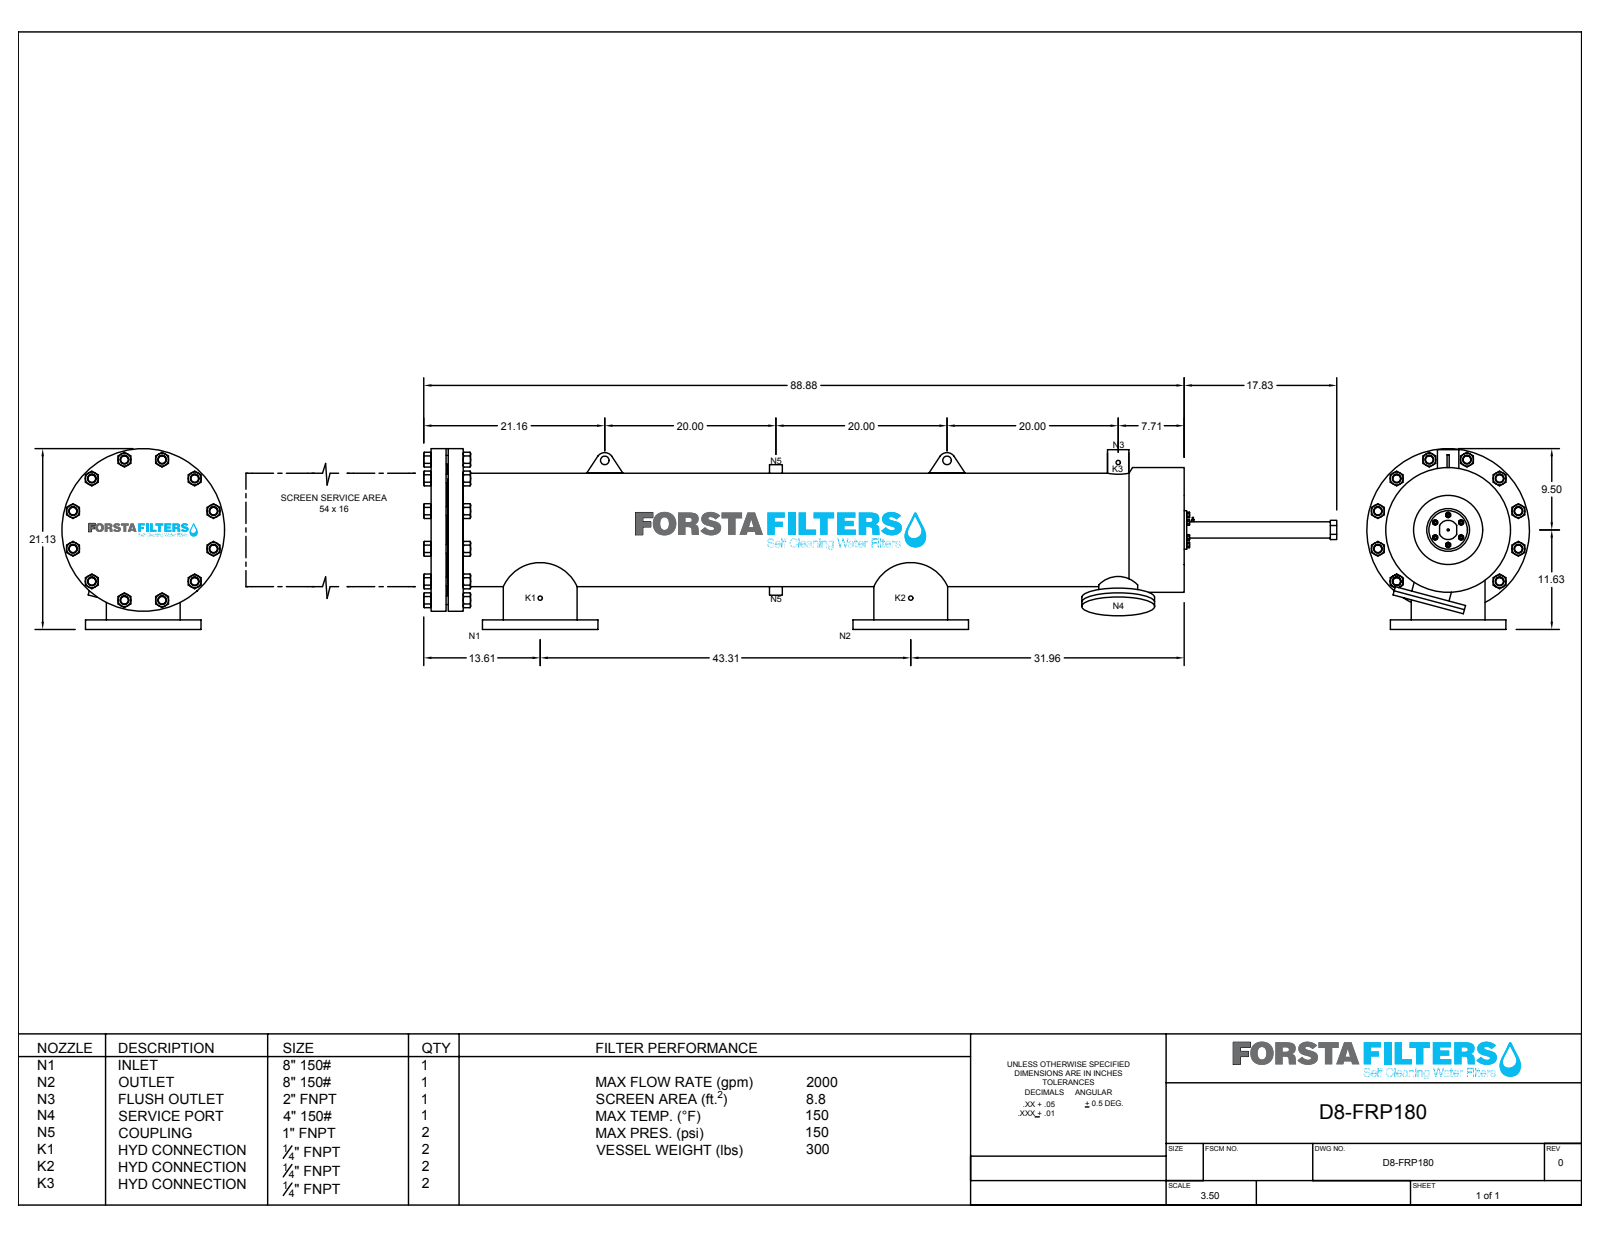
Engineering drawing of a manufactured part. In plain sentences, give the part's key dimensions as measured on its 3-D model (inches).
The part is named "D8-FRP-180". Its 3-D file was written by "SolidWorks 2018 (CONFIG_CONTROL_DESIGN)". It is 19 solids with 661 faces: 297 planar, 342 cylindrical and 22 other. Overall it measures 107.21 by 21.13 by 19 inches. Its volume is 1 930 cubic inches and its surface area 10 916 square inches. Round holes: 16 of diameter 0.75, 16 of diameter 0.88, 15 of diameter 1, 5 of diameter 0.375, 4 of diameter 0.25, 2 of diameter 4, 2 of diameter 8, 1 of diameter 0.375, 1 of diameter 1.506, 1 of diameter 12.86, 1 of diameter 14.187. Round bosses or shafts: 3 of diameter 0.644, 3 of diameter 0.375, 2 of diameter 13.5, 2 of diameter 9, 2 of diameter 8.394, 2 of diameter 4.394, 1 of diameter 19, 1 of diameter 14.581. Partial cylindrical surfaces (rounded edges, fillets, slot ends): 2 of radius 1, 1 of radius 1.125. The main face-to-face distances are 2, 0.5, 88.707, 86.707, 1.12, 88.51, 86.51, 0.197, 3.75, 1.75. The hole center spacings are 2.87, 3.75, 5.303, 6.929, 8.5, 8.309, 5.875, 9.111.
